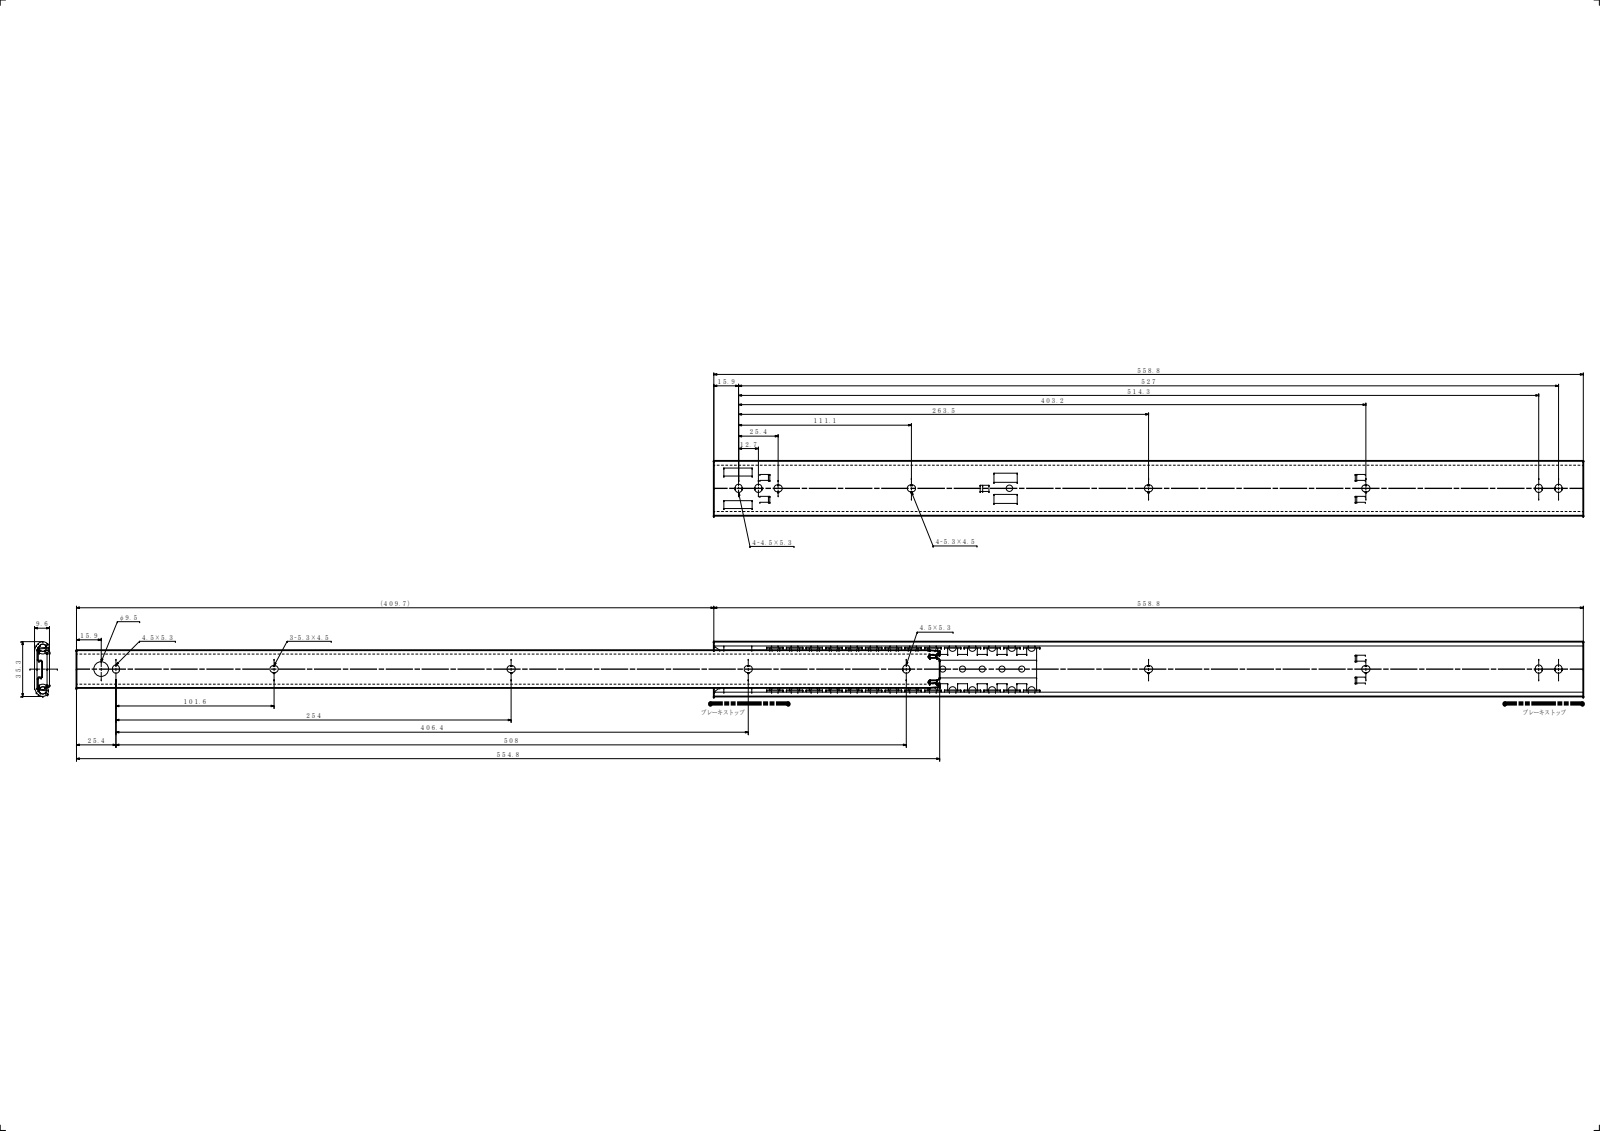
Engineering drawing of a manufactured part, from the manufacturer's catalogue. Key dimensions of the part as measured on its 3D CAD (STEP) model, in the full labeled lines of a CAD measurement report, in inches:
Part name (STEP PRODUCT): IM 3522-22; OM 3522-22; 3522-22
STEP written by: SolidWorks 2019 (CONFIG_CONTROL_DESIGN)
Units: inches
Bodies: 2 solids, 126 faces (58 planar, 68 cylindrical, 0 other)
Overall size (bounding box): 38.13 × 1.39 × 0.378
Volume: 4.267 in³ · Surface area: 142 in²
Round holes (diameter × count): ⌀0.374 ×1
Partial cylindrical surfaces — rounded edges, fillets, slot ends (radius × count): R0.089 ×26, R0.031 ×6, R0.118 ×4, R0.008 ×2, R0.02 ×2, R0.063 ×2, R0.071 ×2, R0.079 ×2
Main face-to-face distances: 0.063, 0.315, 0.252, 0.378, 0.184, 0.121, 0.114, 0.051, 0.201, 0.264
